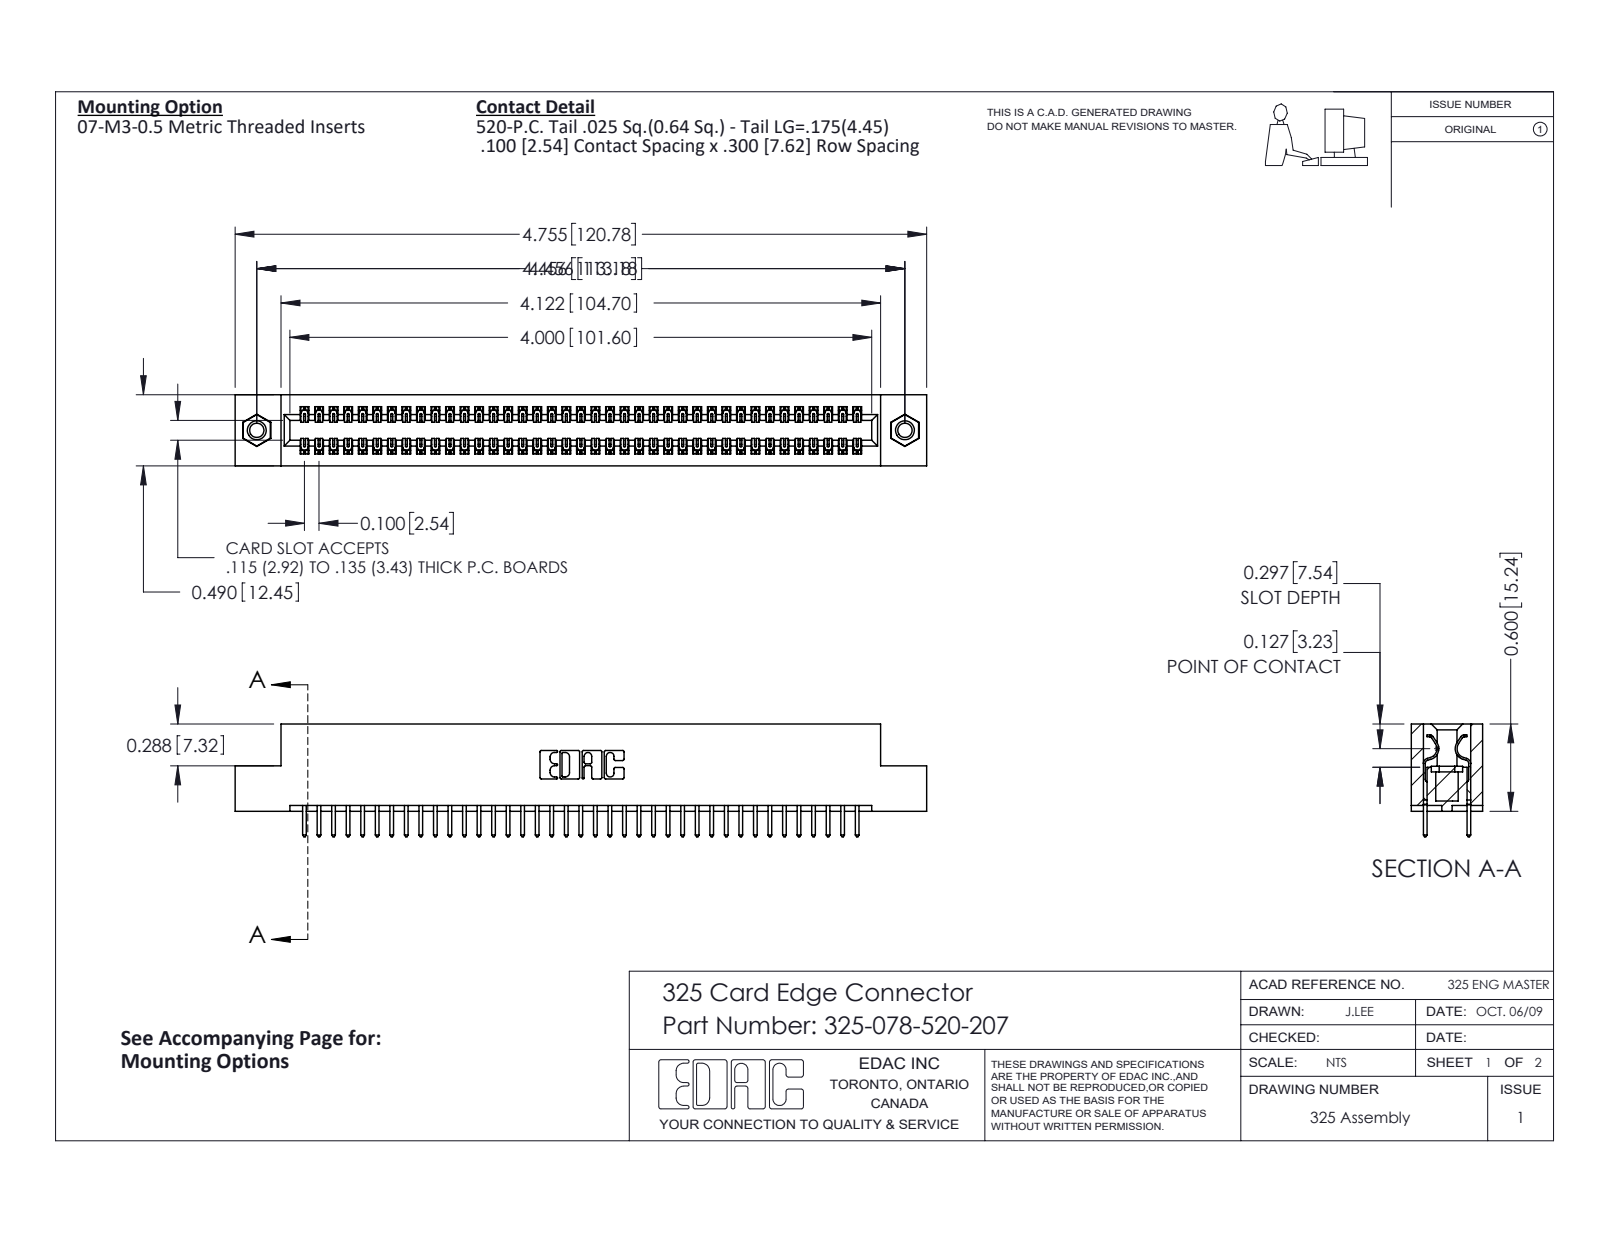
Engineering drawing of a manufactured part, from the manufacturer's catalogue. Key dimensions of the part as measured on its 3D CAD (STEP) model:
Part name (STEP PRODUCT): 345-250-001_345-250-005-103; 325 Part_TI; 325-078-520-207; 325-292-001_325-293-120
STEP written by: SolidWorks 2016 (CONFIG_CONTROL_DESIGN)
Units: inches
Bodies: 81 solids, 4230 faces (2910 planar, 1304 cylindrical, 16 other)
Overall size (bounding box): 4.755 × 0.775 × 0.49
Volume: 0.948 in³ · Surface area: 28.84 in²
Round holes (diameter × count): ⌀0.098 ×2, ⌀0.125 ×2, ⌀0.16 ×2
Round bosses / shafts (diameter × count): ⌀0.155 ×2
Partial cylindrical surfaces — rounded edges, fillets, slot ends (radius × count): R0.006 ×117, R0.01 ×78, R0.01 ×22, R0.007 ×6, R0.031 ×6, R0.026 ×3, R0.014 ×2, R0.022 ×2
Main face-to-face distances: 0.083, 0.407, 0.49, 0.3, 0.107, 0.383, 0.025, 0.325, 0.275, 0.56
Hole centre spacings: 4.456
